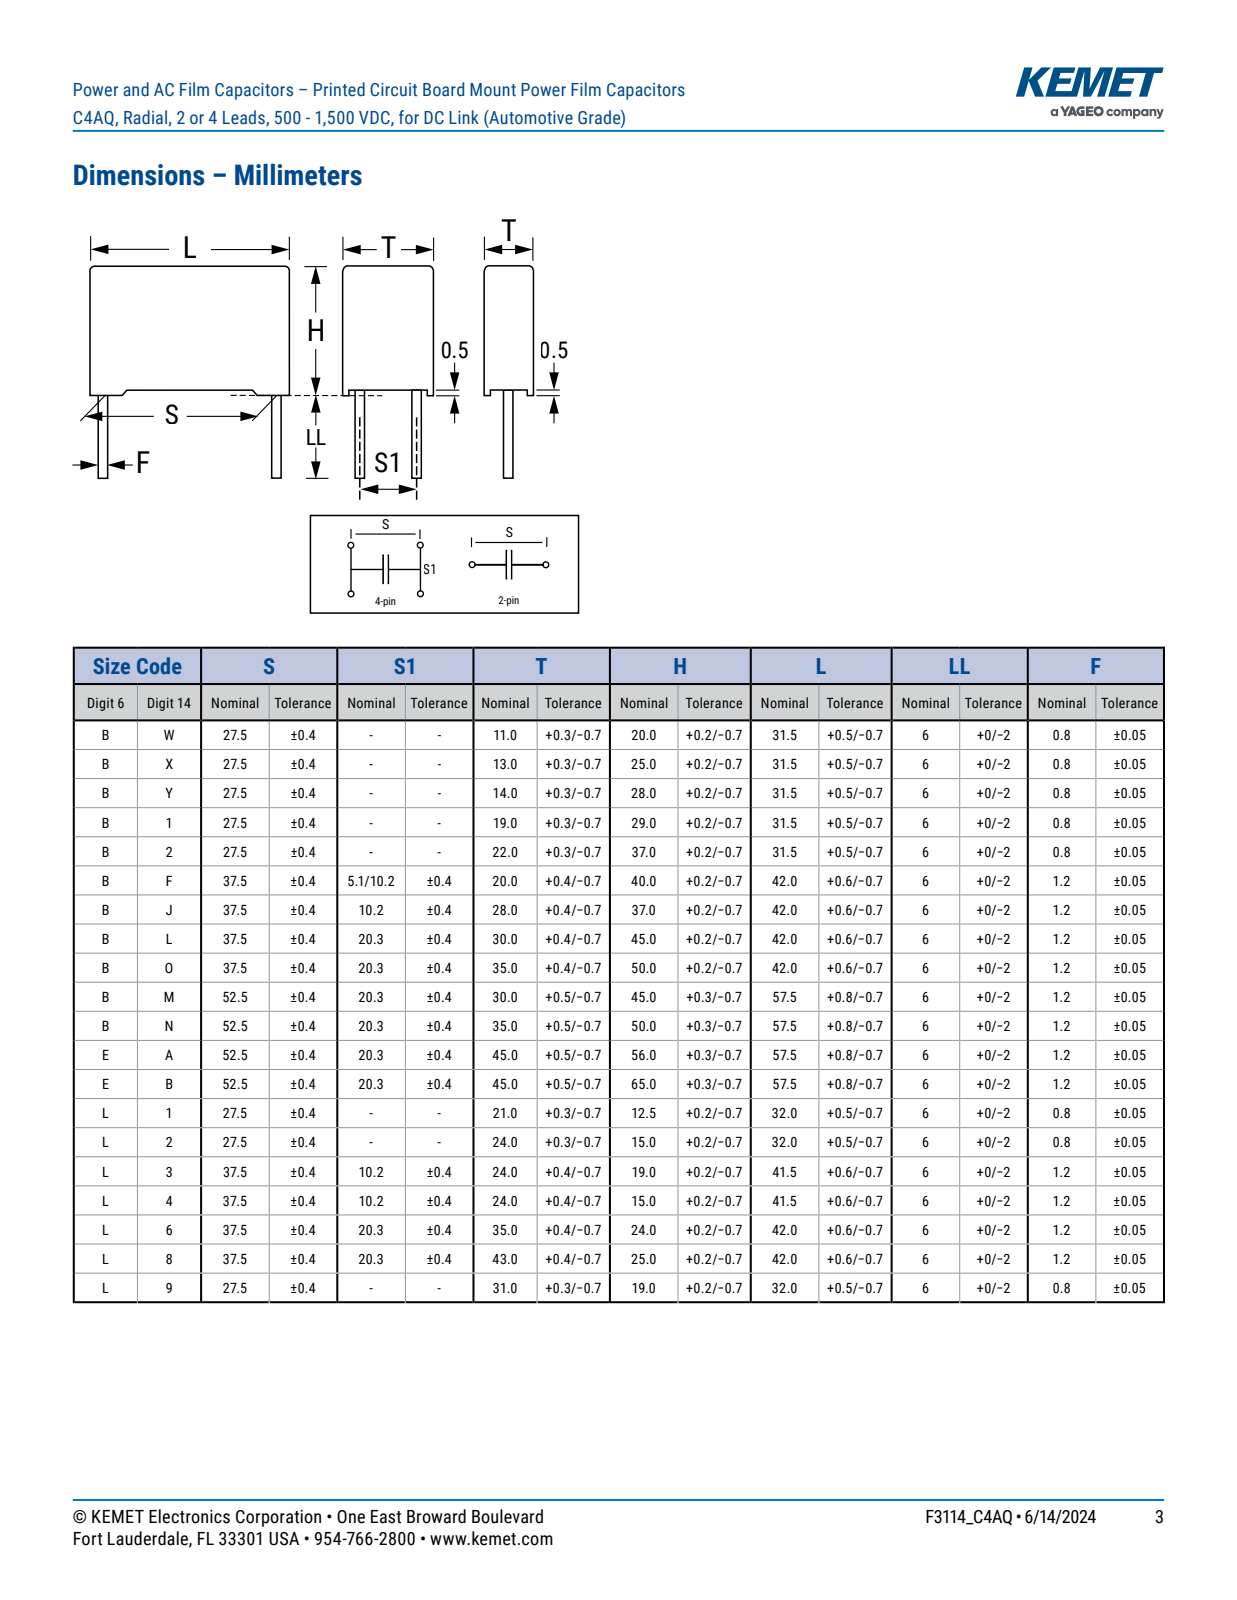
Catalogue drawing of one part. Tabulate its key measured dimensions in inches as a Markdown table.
| quantity | value |
| --- | --- |
| part name | CFP_RB4_57.5X65X45_L58.3H65.3T45.5S52.5S120.3LL6F1.25 |
| STEP written by | SolidWorks 2014 (AUTOMOTIVE_DESIGN) |
| units | inches |
| bodies | 4 solids, 91 faces (83 planar, 8 cylindrical, 0 other) |
| overall size | 2.807 × 2.295 × 1.792 |
| volume | 10.3 in³ |
| surface area | 29.8 in² |
| round bosses / shafts (diameter × count) | 0.049 × 4 |
| main face-to-face distances | 1.791, 2.295, 2.495, 0.076, 2.571, 0.11, 2.185, 2.075, 1.681, 1.571 |
